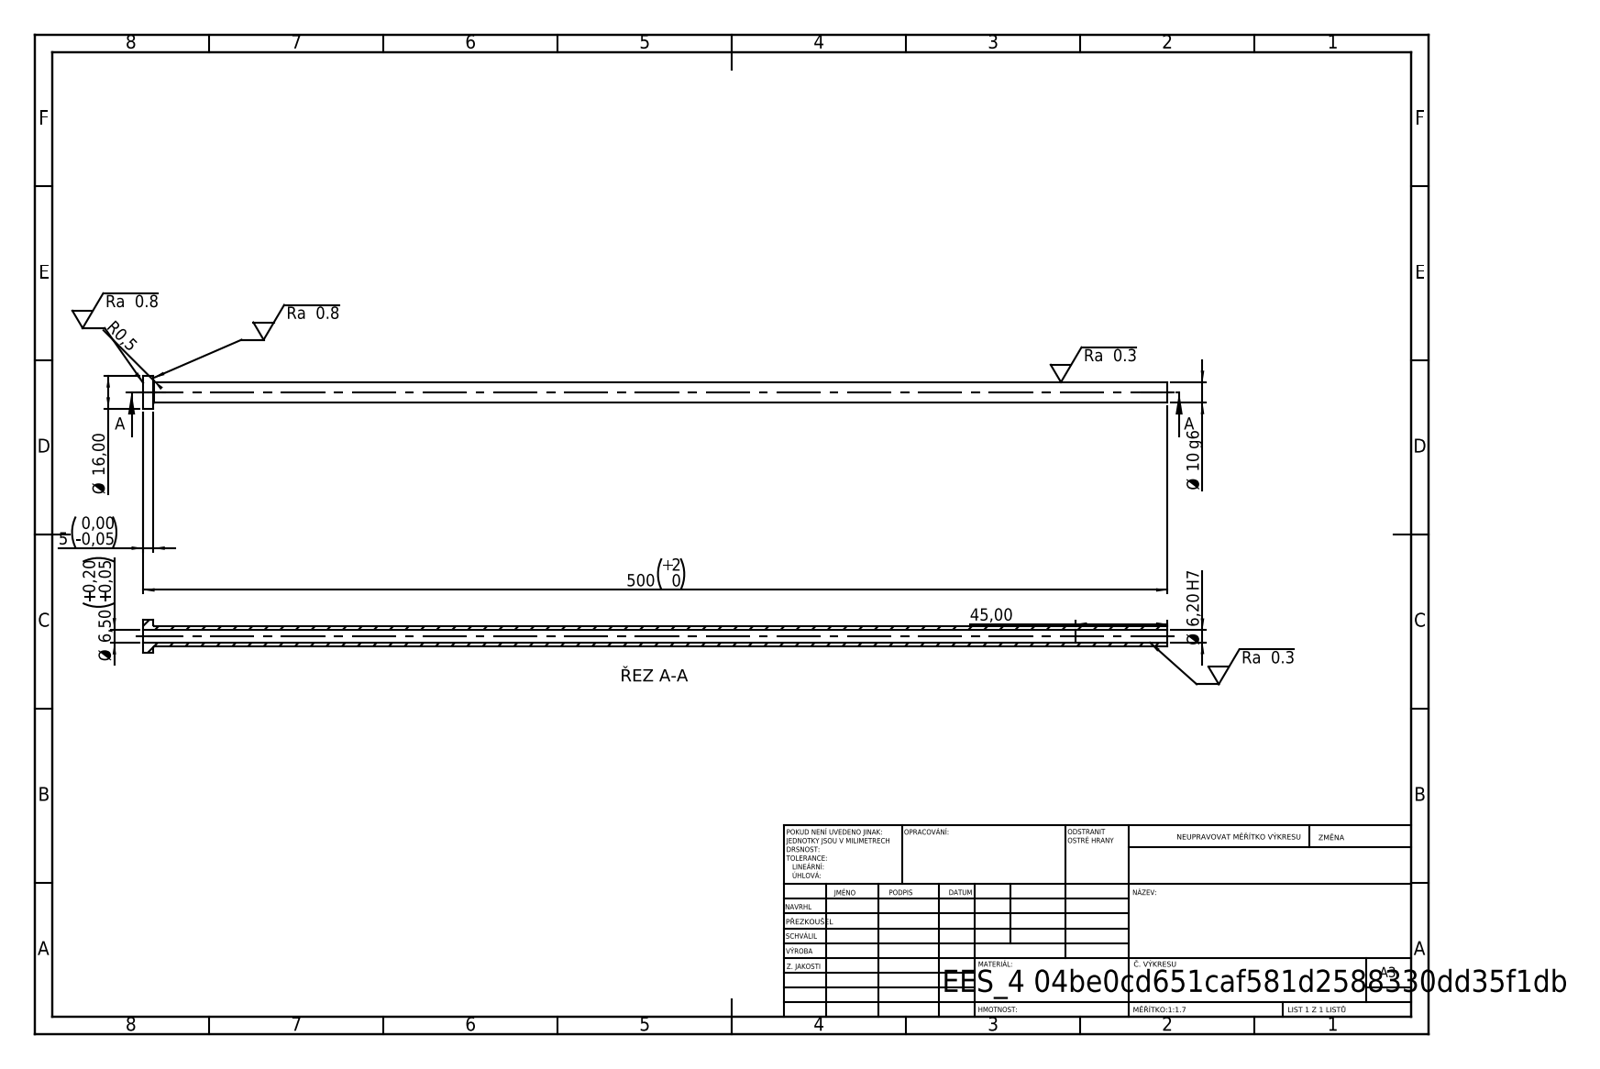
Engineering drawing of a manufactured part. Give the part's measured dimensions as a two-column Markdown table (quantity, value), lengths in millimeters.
| quantity | value |
| --- | --- |
| STEP written by | SolidWorks 2019 (CONFIG_CONTROL_DESIGN) |
| units | millimeters |
| bodies | 1 solid, 14 faces (4 planar, 8 cylindrical, 2 other) |
| overall size | 500 × 16 × 16 |
| volume | 23 427 mm³ |
| surface area | 26 305 mm² |
| round holes (diameter × count) | 6.2 × 1, 6.5 × 1 |
| round bosses / shafts (diameter × count) | 16 × 1, 10 × 1 |
| main face-to-face distances | 5, 500, 495, 455, 450, 45 |
